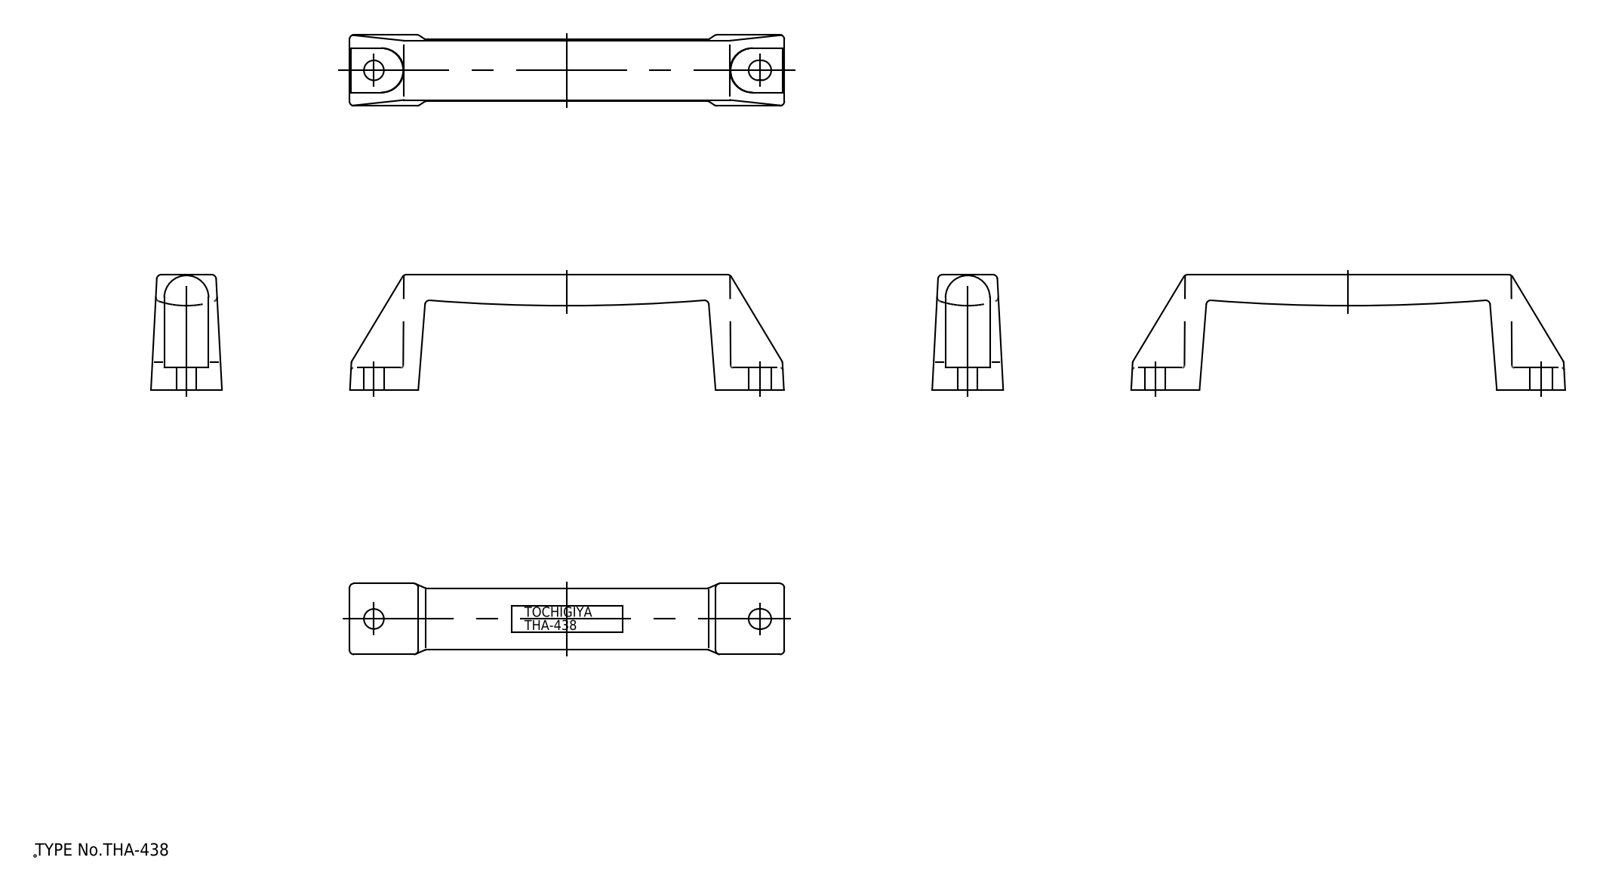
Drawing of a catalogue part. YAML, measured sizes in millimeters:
step_written_by: "spGate 19.8.4 (****-****-****-****) (AUTOMOTIVE_DESIGN)"
units: millimeters
bodies: {solids: 1, faces: 80, planar: 21, cylindrical: 35, other: 24}
overall_size: [98, 26, 16]
volume: 12233
surface_area: 6244
round_holes:
  - {diameter: 4.5, count: 1}
partial_cylinders:
  - {radius: 1, count: 20}
  - {radius: 0.5, count: 4}
  - {radius: 2.25, count: 2}
  - {radius: 5, count: 2}
  - {radius: 395, count: 1}
face_to_face_distances: [26, 5, 21, 10, 2.75, 7.25, 4.5]
